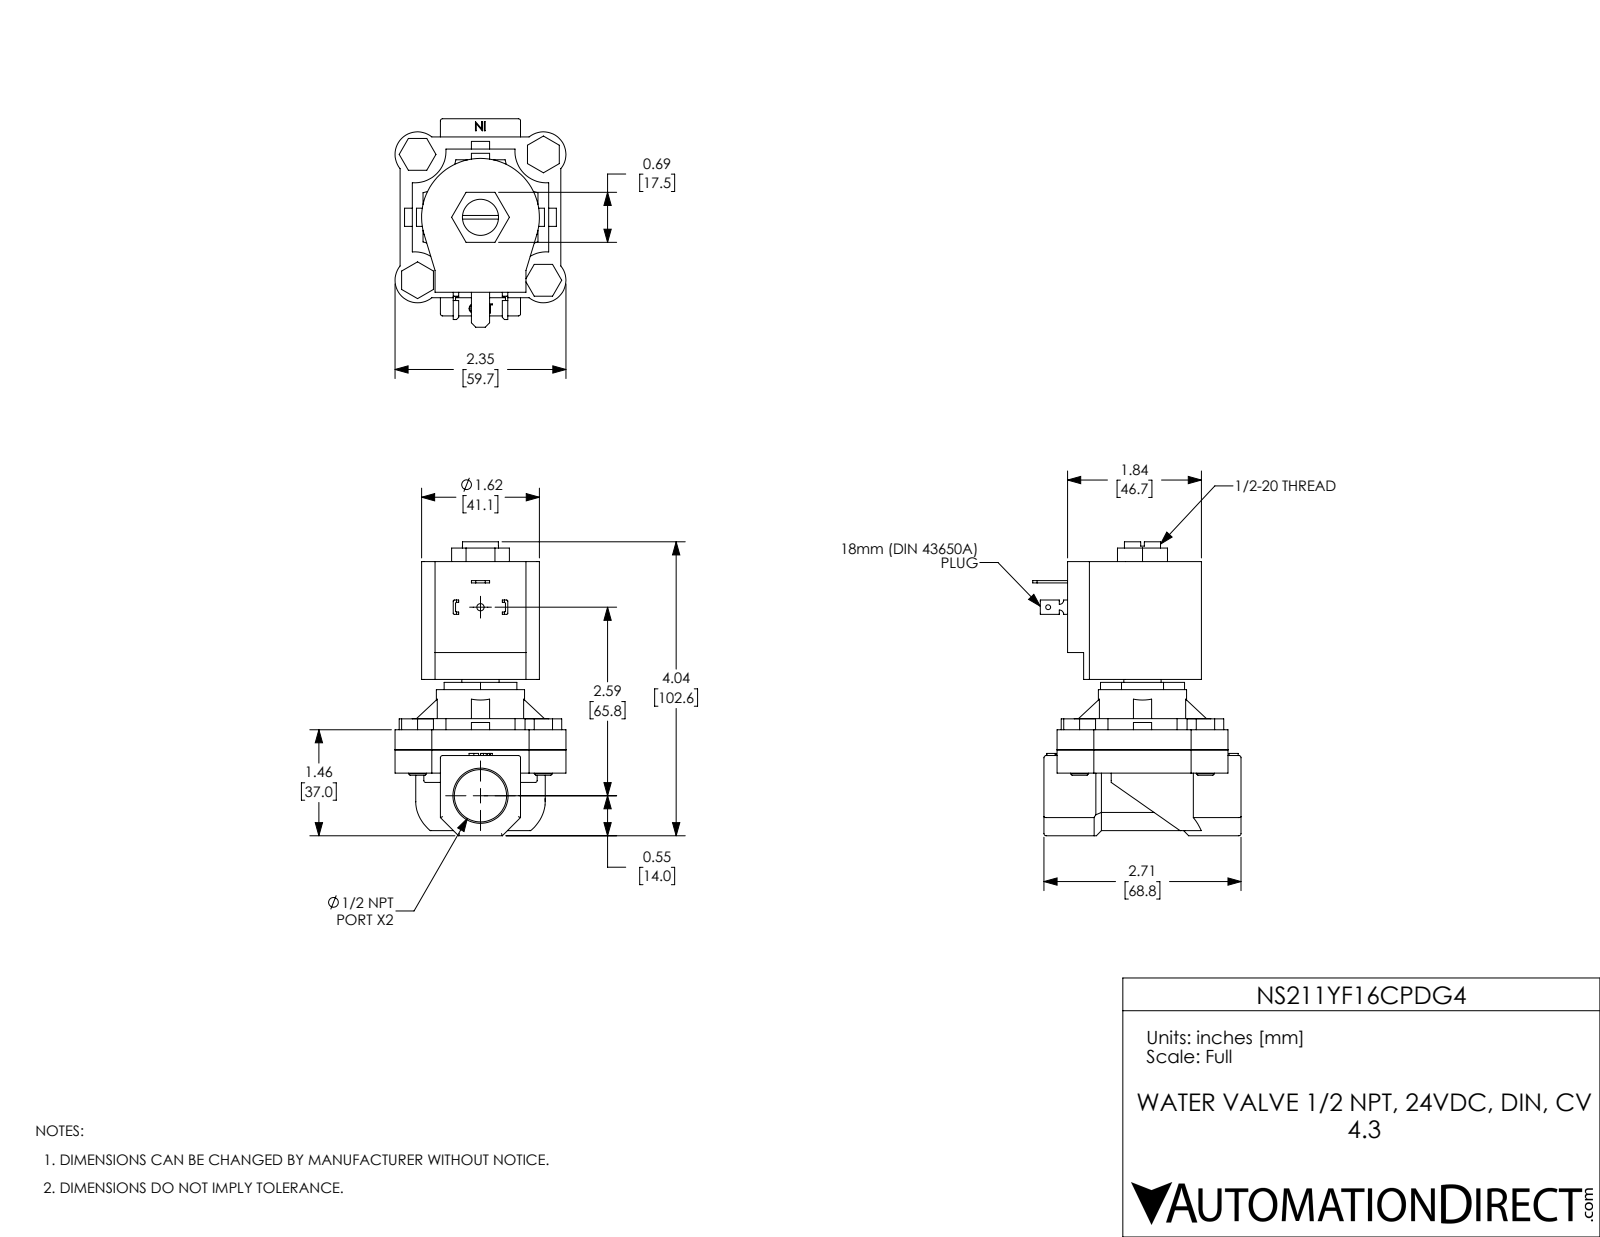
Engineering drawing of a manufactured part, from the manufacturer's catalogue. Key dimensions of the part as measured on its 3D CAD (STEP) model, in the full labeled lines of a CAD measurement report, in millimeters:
Part name (STEP PRODUCT): NS211YF16CPDG4
STEP written by: SolidWorks 2021 (CONFIG_CONTROL_DESIGN)
Units: millimetres
Bodies: 11 solids, 385 faces (239 planar, 113 cylindrical, 33 other)
Overall size (bounding box): 102.6 × 72.8 × 59.7
Volume: 165 500 mm³ · Surface area: 43 680 mm²
Round holes (diameter × count): ⌀6.4 ×4, ⌀1.7 ×1, ⌀2.5 ×1, ⌀12.6 ×1, ⌀13 ×1, ⌀18.3 ×1, ⌀29.3 ×1
Round bosses / shafts (diameter × count): ⌀6.3 ×4, ⌀30.8 ×1
Partial cylindrical surfaces — rounded edges, fillets, slot ends (radius × count): R0.8 ×15, R0.4 ×8, R7.9 ×4, R11 ×4, R14.7 ×4, R1.5 ×2, R20.6 ×1, R22.6 ×1
Main face-to-face distances: 7, 65.7, 58.7, 8.1, 15.1, 73.8, 14.1, 42.1, 6.4, 56.1
Hole centre spacings: 31.1, 43.9, 62.1, 65.8
